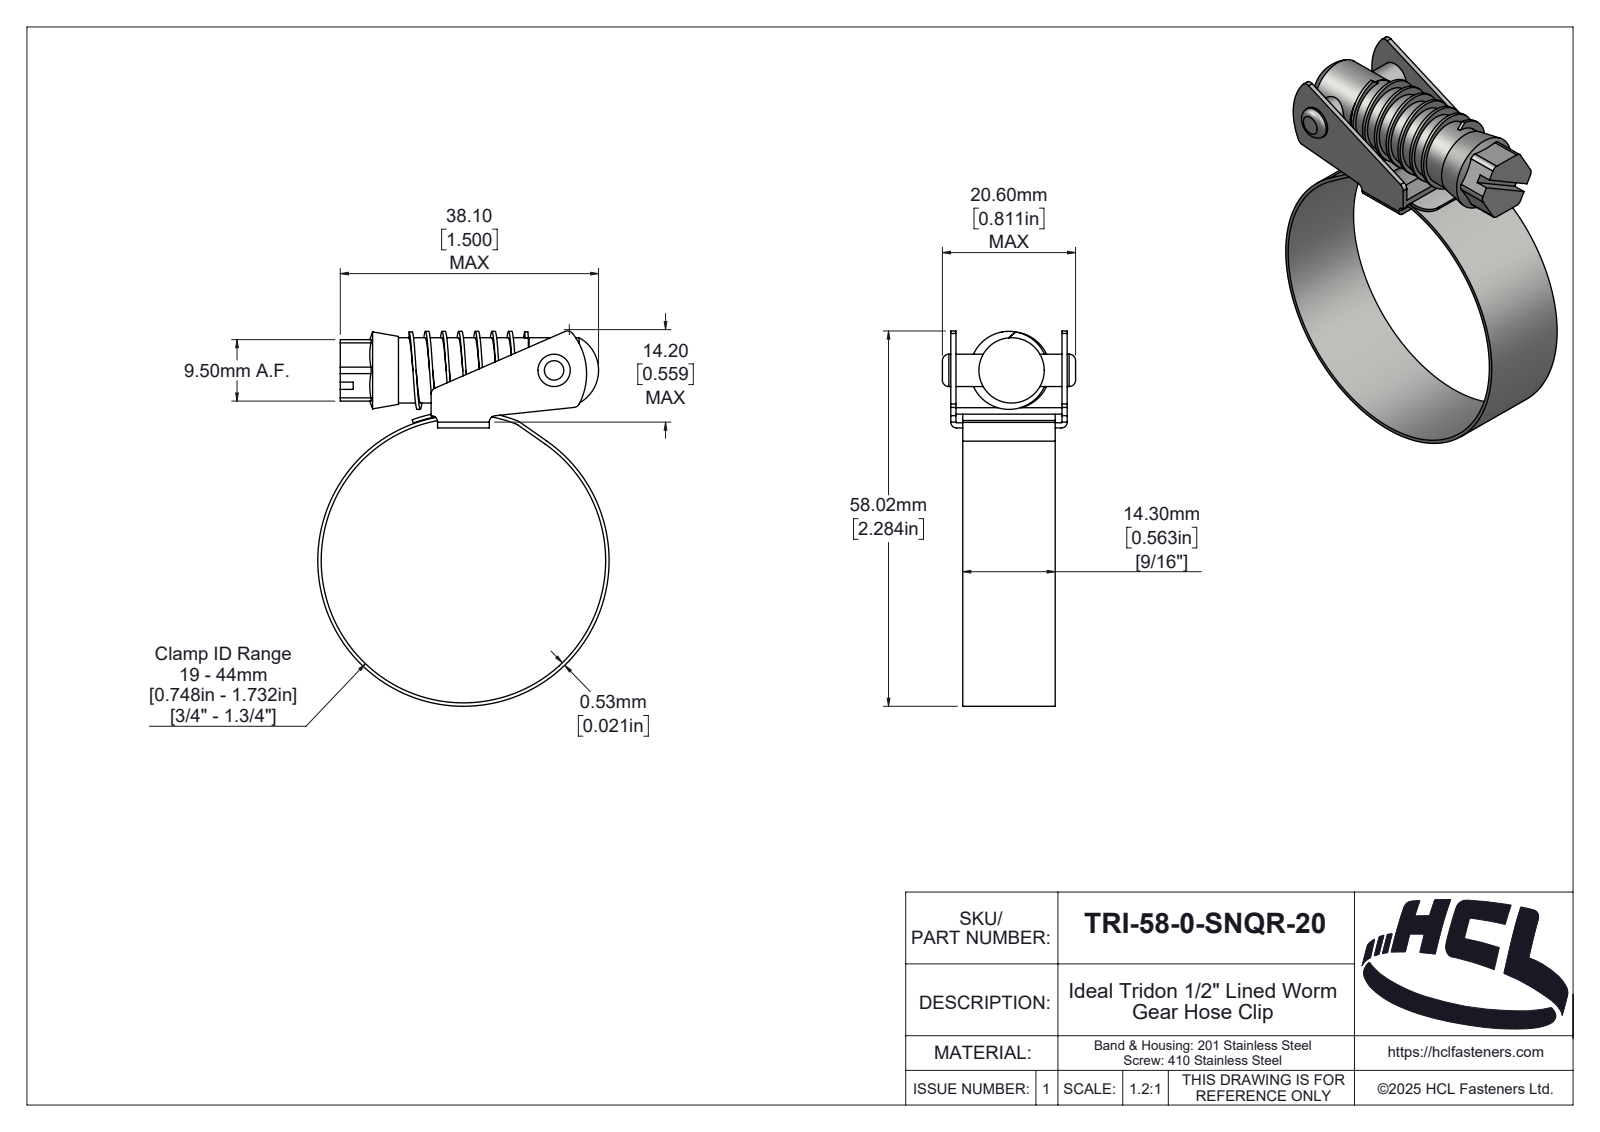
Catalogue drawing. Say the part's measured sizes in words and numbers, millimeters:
The part is named "TRI-58-0-SNQR-20". Its 3-D file was written by "SolidWorks 2025 (AUTOMOTIVE_DESIGN)". It is 5 solids with 222 faces: 44 planar, 112 cylindrical and 66 other. Overall it measures 58.02 by 45.06 by 20.6 millimeters. Its volume is 4 944 cubic millimeters and its surface area 8 344 square millimeters. Round holes: 1 of diameter 5, 1 of diameter 44. Round bosses or shafts: 1 of diameter 45.06, 1 of diameter 10.1. Partial cylindrical surfaces (rounded edges, fillets, slot ends): 11 of radius 1, 2 of radius 0.1, 2 of radius 0.9, 2 of radius 3, 1 of radius 0.46, 1 of radius 1.89, 1 of radius 2, 1 of radius 2.35. The main face-to-face distances are 0.8, 17.2, 18, 16.4, 1.85, 16.15, 1.05, 15.35, 1, 2.13. The hole center spacings are 32.57.
